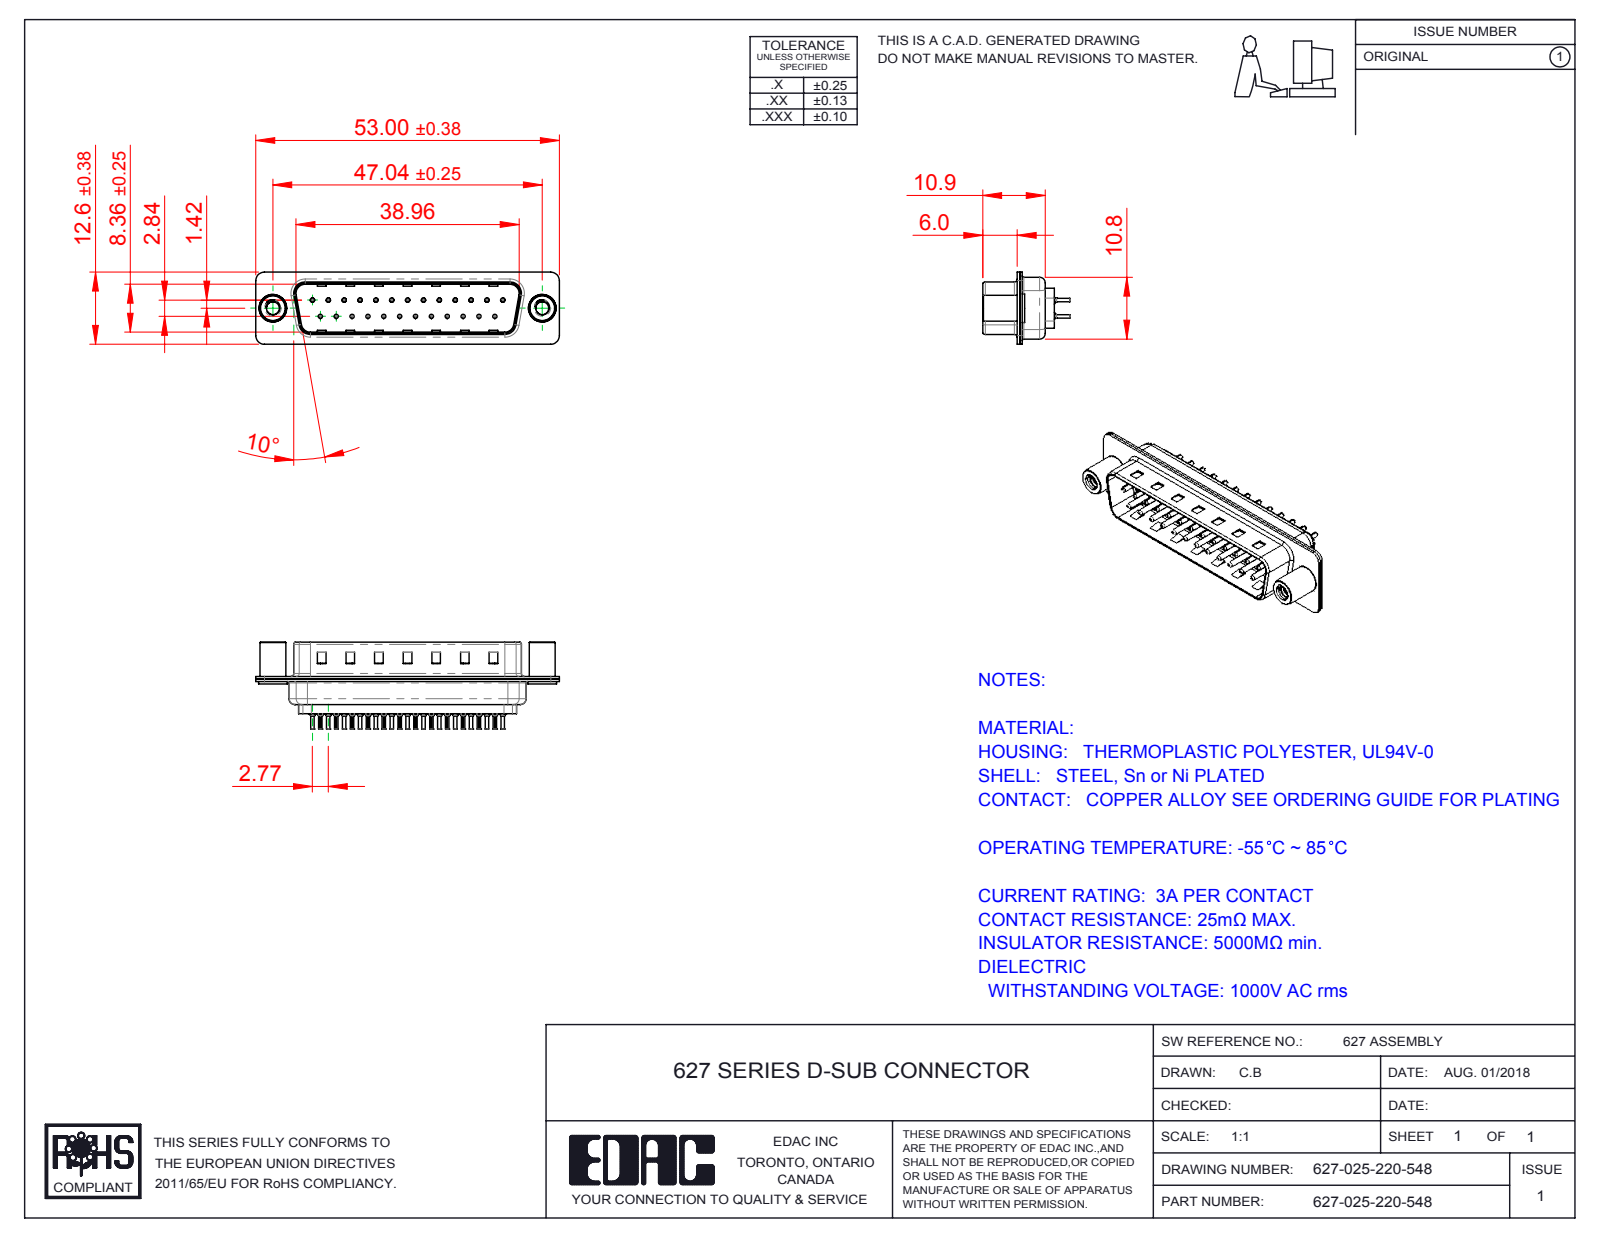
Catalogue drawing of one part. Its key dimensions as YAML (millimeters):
part_name: "627-025-220-548; 627 Contact Row 2_20L; 627 4-40 Threaded Standoff; 627 Contact Row 1_20L (+3 more)"
step_written_by: "SolidWorks 2016 (CONFIG_CONTROL_DESIGN)"
units: millimeters
bodies: {solids: 30, faces: 2860, planar: 773, cylindrical: 1090, other: 997}
overall_size: [53, 15.2, 12.6]
volume: 2733
surface_area: 7853
round_holes:
  - {diameter: 0.2, count: 25}
  - {diameter: 0.35, count: 25}
  - {diameter: 1.1, count: 25}
  - {diameter: 1.6, count: 25}
  - {diameter: 2.26, count: 2}
  - {diameter: 4, count: 2}
  - {diameter: 4.8, count: 2}
round_bosses_or_shafts:
  - {diameter: 2, count: 25}
  - {diameter: 1.5, count: 25}
  - {diameter: 0.75, count: 25}
  - {diameter: 0.6, count: 25}
  - {diameter: 5, count: 2}
  - {diameter: 4.9, count: 2}
  - {diameter: 4.5, count: 2}
partial_cylinders:
  - {radius: 0.1, count: 50}
  - {radius: 1.5, count: 16}
  - {radius: 2, count: 12}
  - {radius: 0.5, count: 8}
  - {radius: 1.6, count: 8}
  - {radius: 0.25, count: 4}
  - {radius: 0.6, count: 4}
  - {radius: 0.65, count: 4}
face_to_face_distances: [0.4, 0.45, 0.82, 9.58, 0.9, 8.76, 1.5, 1.4, 6.5, 6.05]
hole_center_spacings: [3.16, 8.31, 2.77, 5.54, 11.08, 16.62, 5.03, 5.04]
